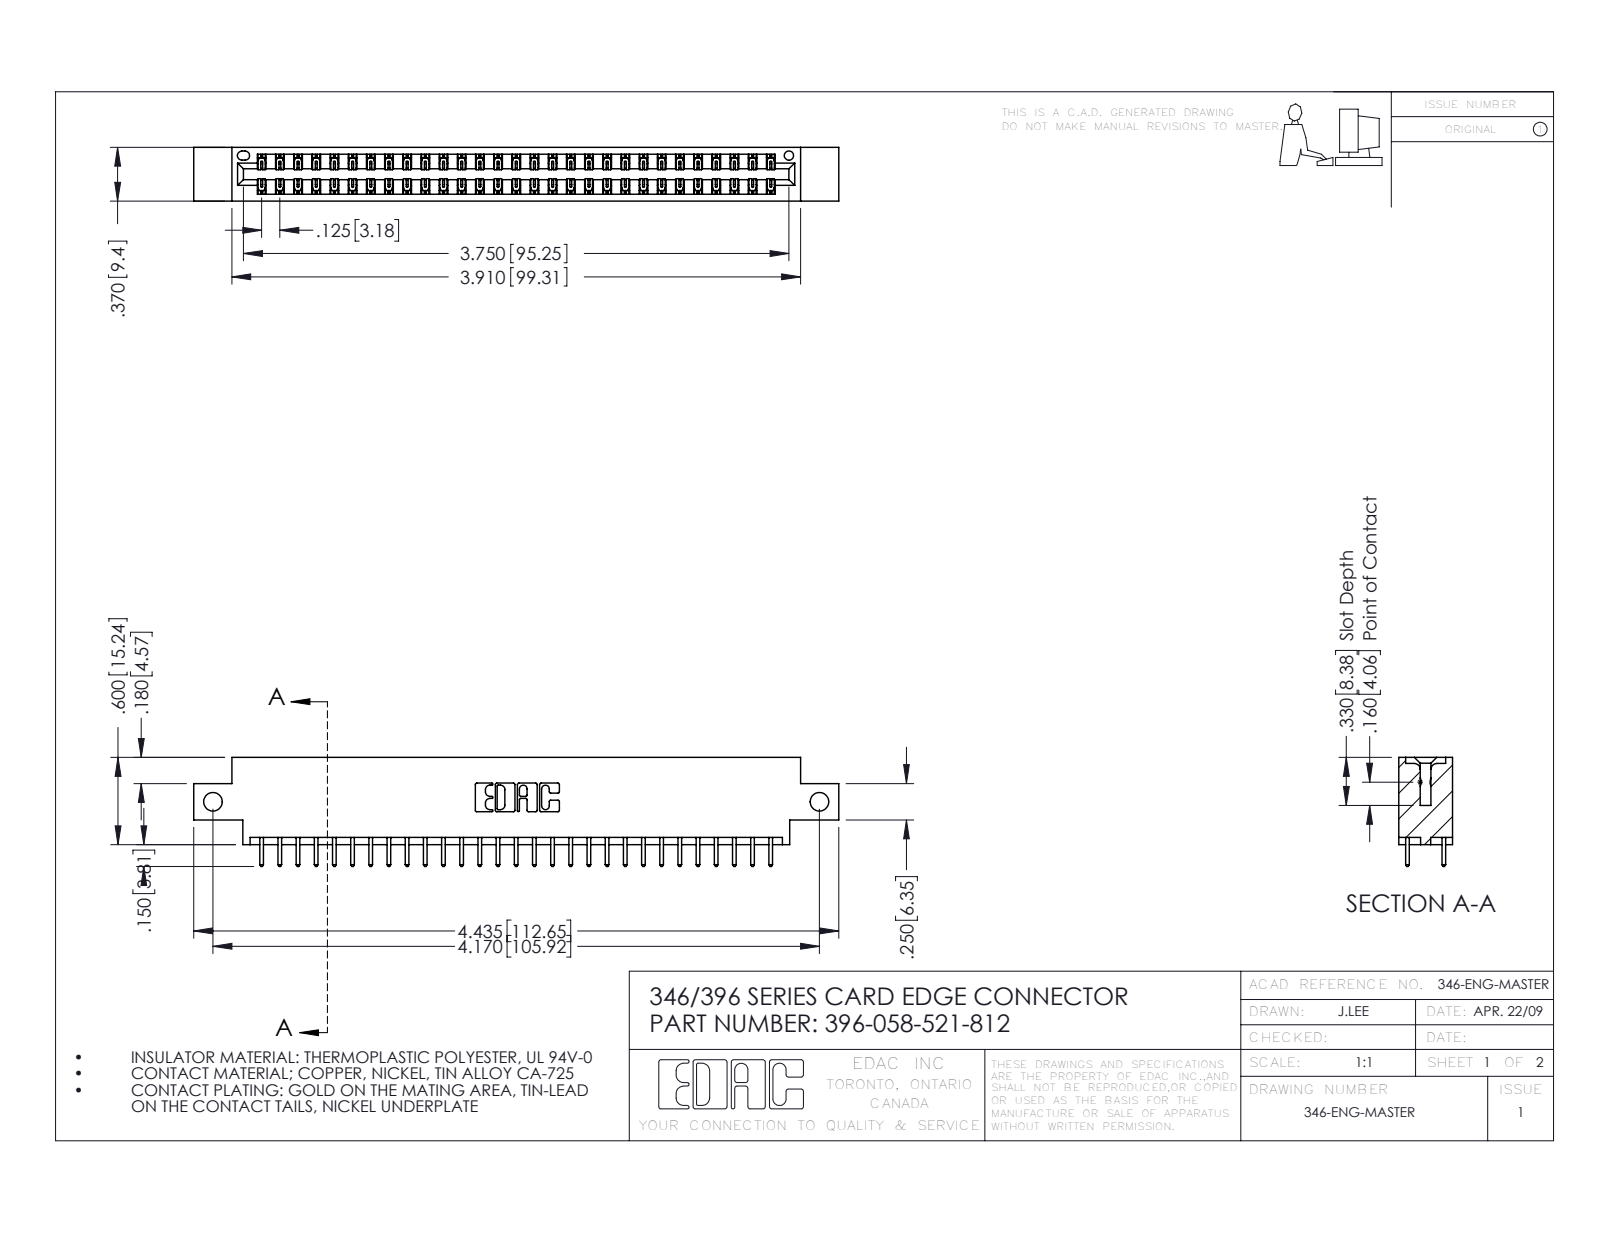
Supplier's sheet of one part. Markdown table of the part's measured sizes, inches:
| quantity | value |
| --- | --- |
| part name | 396-058-521-812; 345-292-001_345-293-121; 346 Part_0.170 Offset - Side Mount |
| STEP written by | SolidWorks 2016 (CONFIG_CONTROL_DESIGN) |
| units | inches |
| bodies | 59 solids, 3142 faces (2110 planar, 1032 cylindrical, 0 other) |
| overall size | 4.435 × 0.75 × 0.37 |
| volume | 0.648 in³ |
| surface area | 22.12 in² |
| round holes (diameter × count) | 0.128 × 2, 0.064 × 1 |
| partial cylindrical surfaces (radius × count) | 0.006 × 87, 0.01 × 58, 0.01 × 22, 0.007 × 6, 0.031 × 6, 0.026 × 3, 0.014 × 2, 0.022 × 2 |
| main face-to-face distances | 0.048, 0.322, 0.37, 0.25, 0.072, 0.298, 0.025, 0.275, 0.148, 0.222 |
| hole center spacings | 4.17 |
